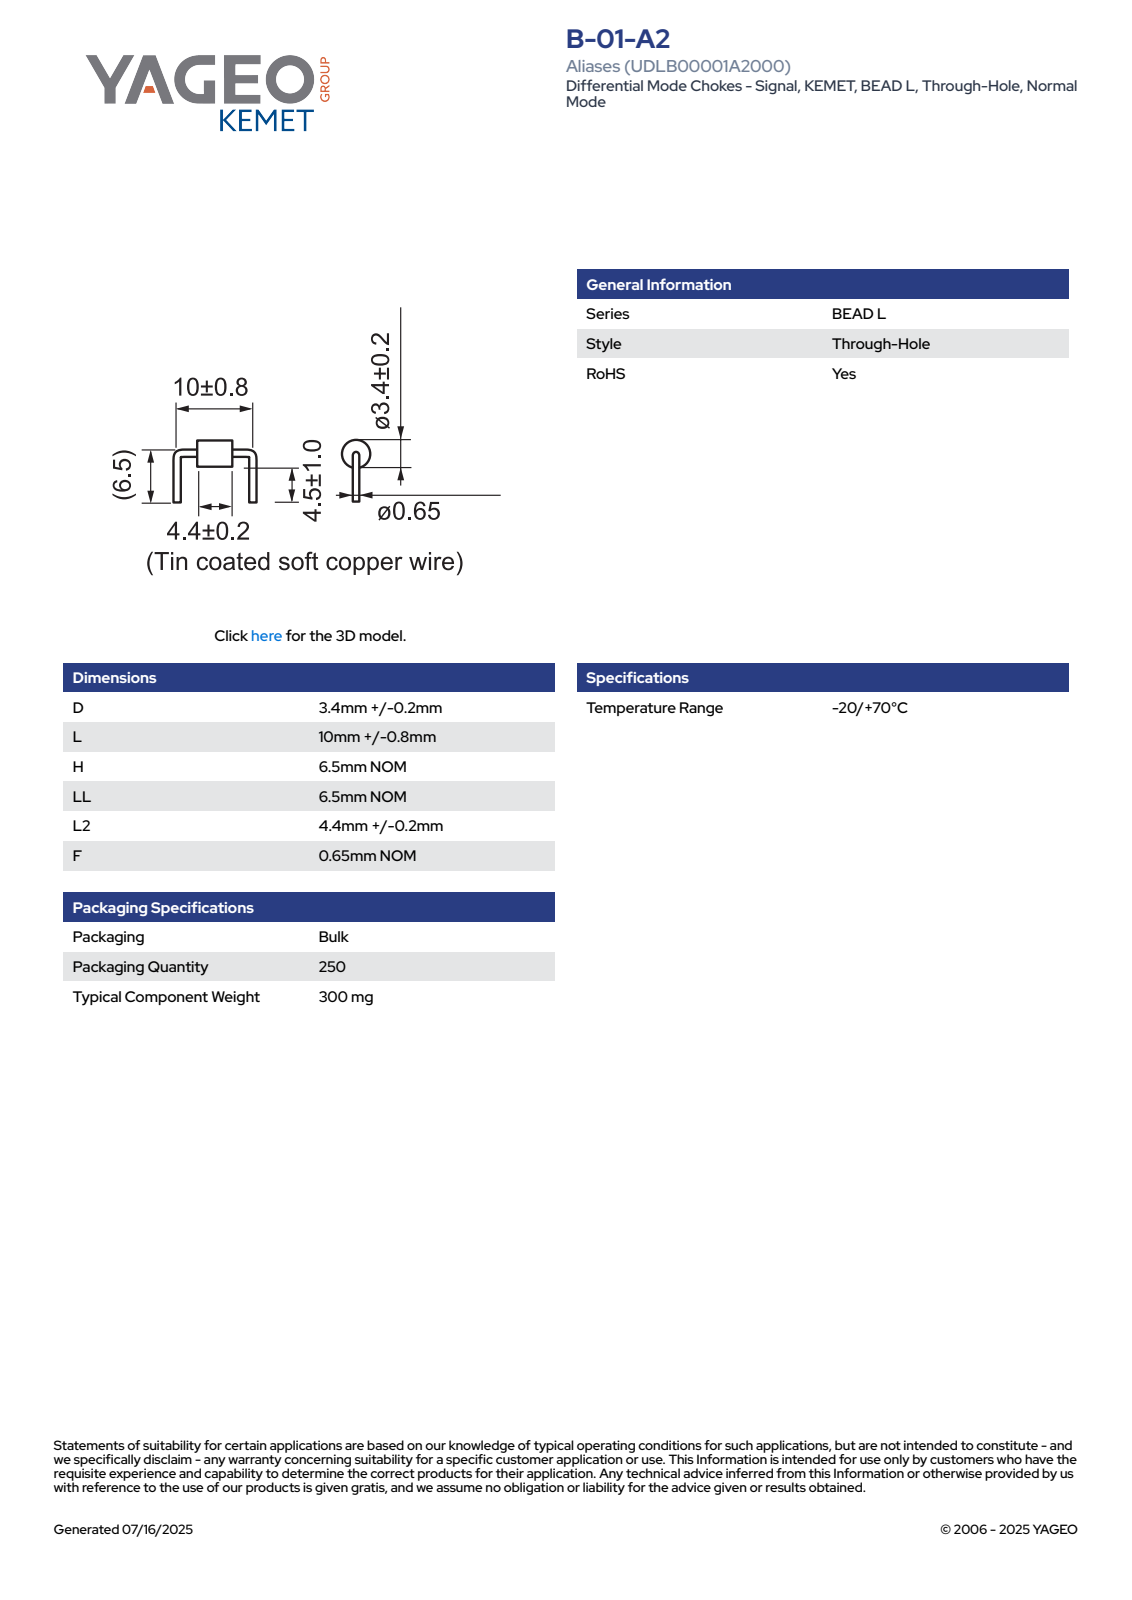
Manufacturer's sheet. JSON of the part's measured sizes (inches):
{"part_name": "IL_B01A1_D3.6L10.8L24.6H6.5LL6.5", "step_written_by": "SolidWorks 2014 (AUTOMOTIVE_DESIGN)", "units": "inches", "bodies": {"solids": 1, "faces": 72, "planar": 26, "cylindrical": 13, "other": 33}, "overall_size": [0.425, 0.327, 0.142], "volume_in3": 0.003, "surface_area_in2": 0.171, "round_bosses_or_shafts": [[0.026, 3], [0.142, 1]], "partial_cylinders_radius": [[0.071, 1]], "face_to_face_distances": [0.181]}
